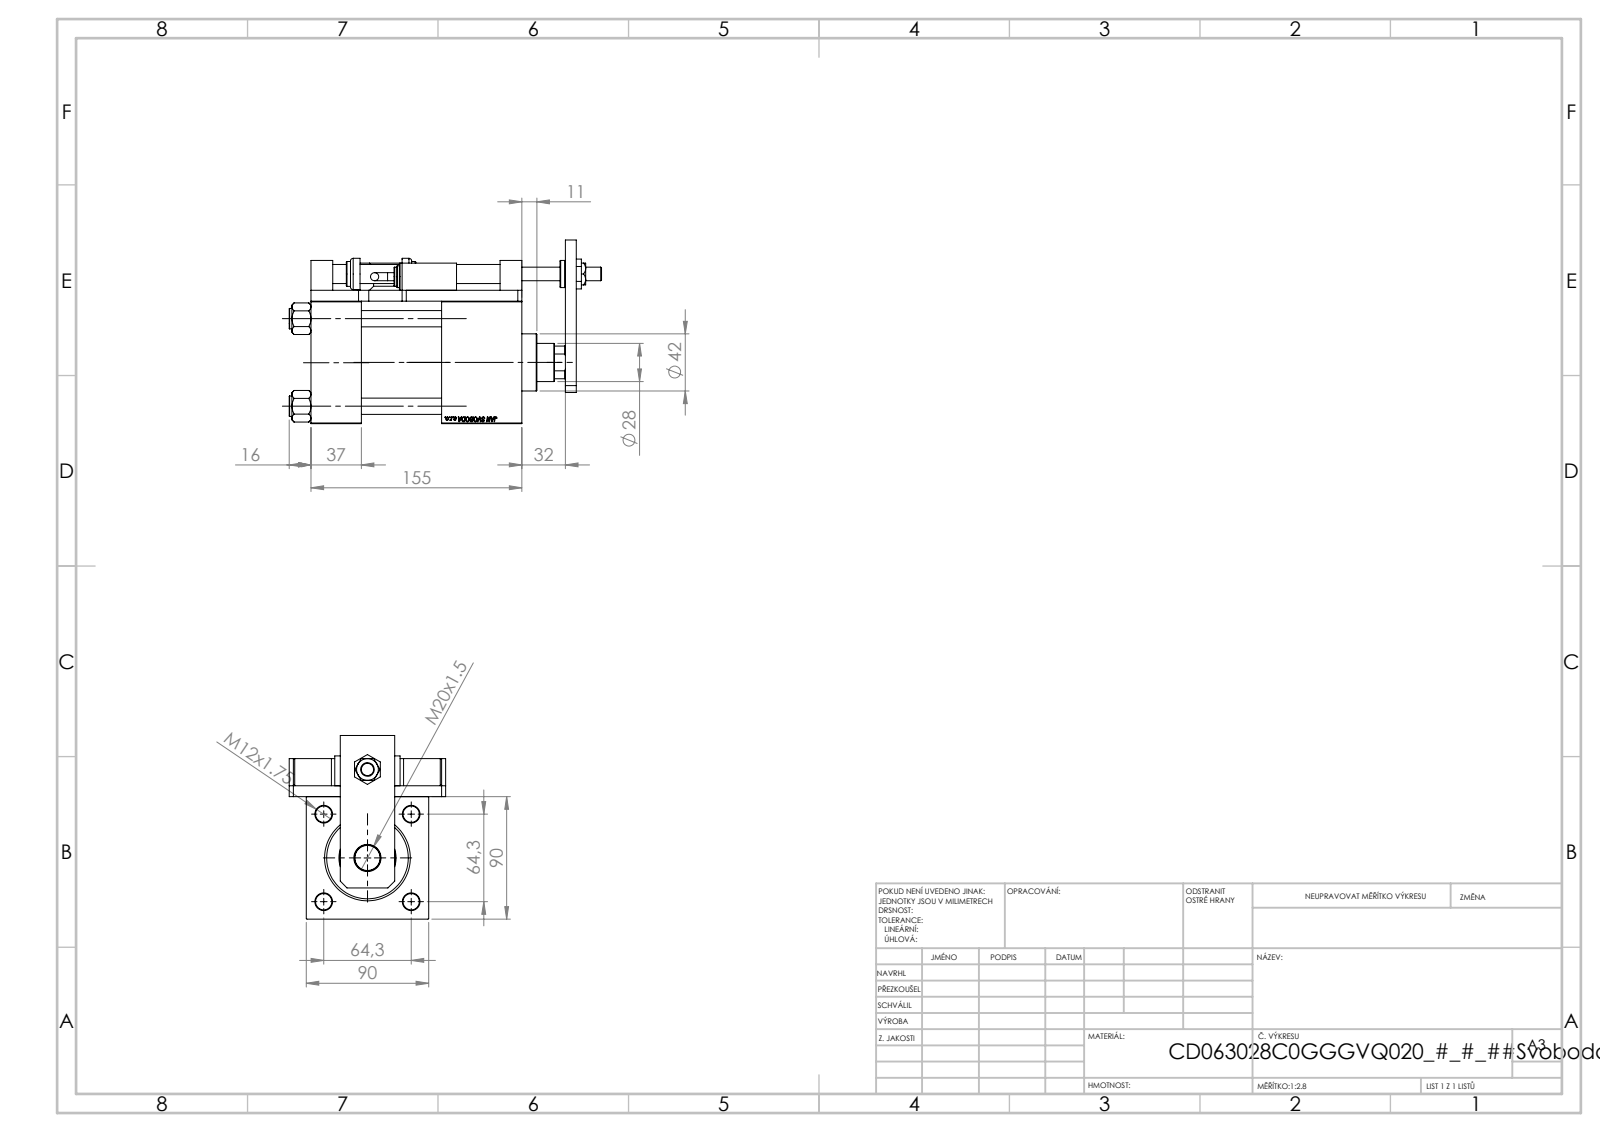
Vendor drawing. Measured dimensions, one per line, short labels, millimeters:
name: V215CD_SWITCH_Q_DIMA; V215CD_SWITCH_Q_PODLOZKA_FRONT; V215CD_SWITCH_Q_SWITCH; V215CD_SWITCH_Q_ZARAZKA (+8 more)
written by: SolidWorks 2019 (CONFIG_CONTROL_DESIGN)
unit: mm
bodies: 24 solids, 1377 faces (647 planar, 155 cylindrical, 575 other)
size: 229.5 × 135 × 115
volume: 1 212 000 mm³; area: 264 374 mm²
holes: 4× ⌀8.5, 4× ⌀12, 4× ⌀13.5, 2× ⌀7, 2× ⌀20.96, 2× ⌀30, 1× ⌀10, 1× ⌀14, 1× ⌀18.5, 1× ⌀20, 1× ⌀28, 1× ⌀31
bosses: 4× ⌀15, 3× ⌀20, 2× ⌀16, 2× ⌀14, 2× ⌀6, 1× ⌀69, 1× ⌀42, 1× ⌀23
rounds: 4× R7.5, 1× R13.5
face distances: 8, 90, 118, 59, 37, 98, 155, 20, 32, 40
hole spacings: 45.47, 64.3, 19.14, 32, 34.89, 45.96, 90.93, 102.33
